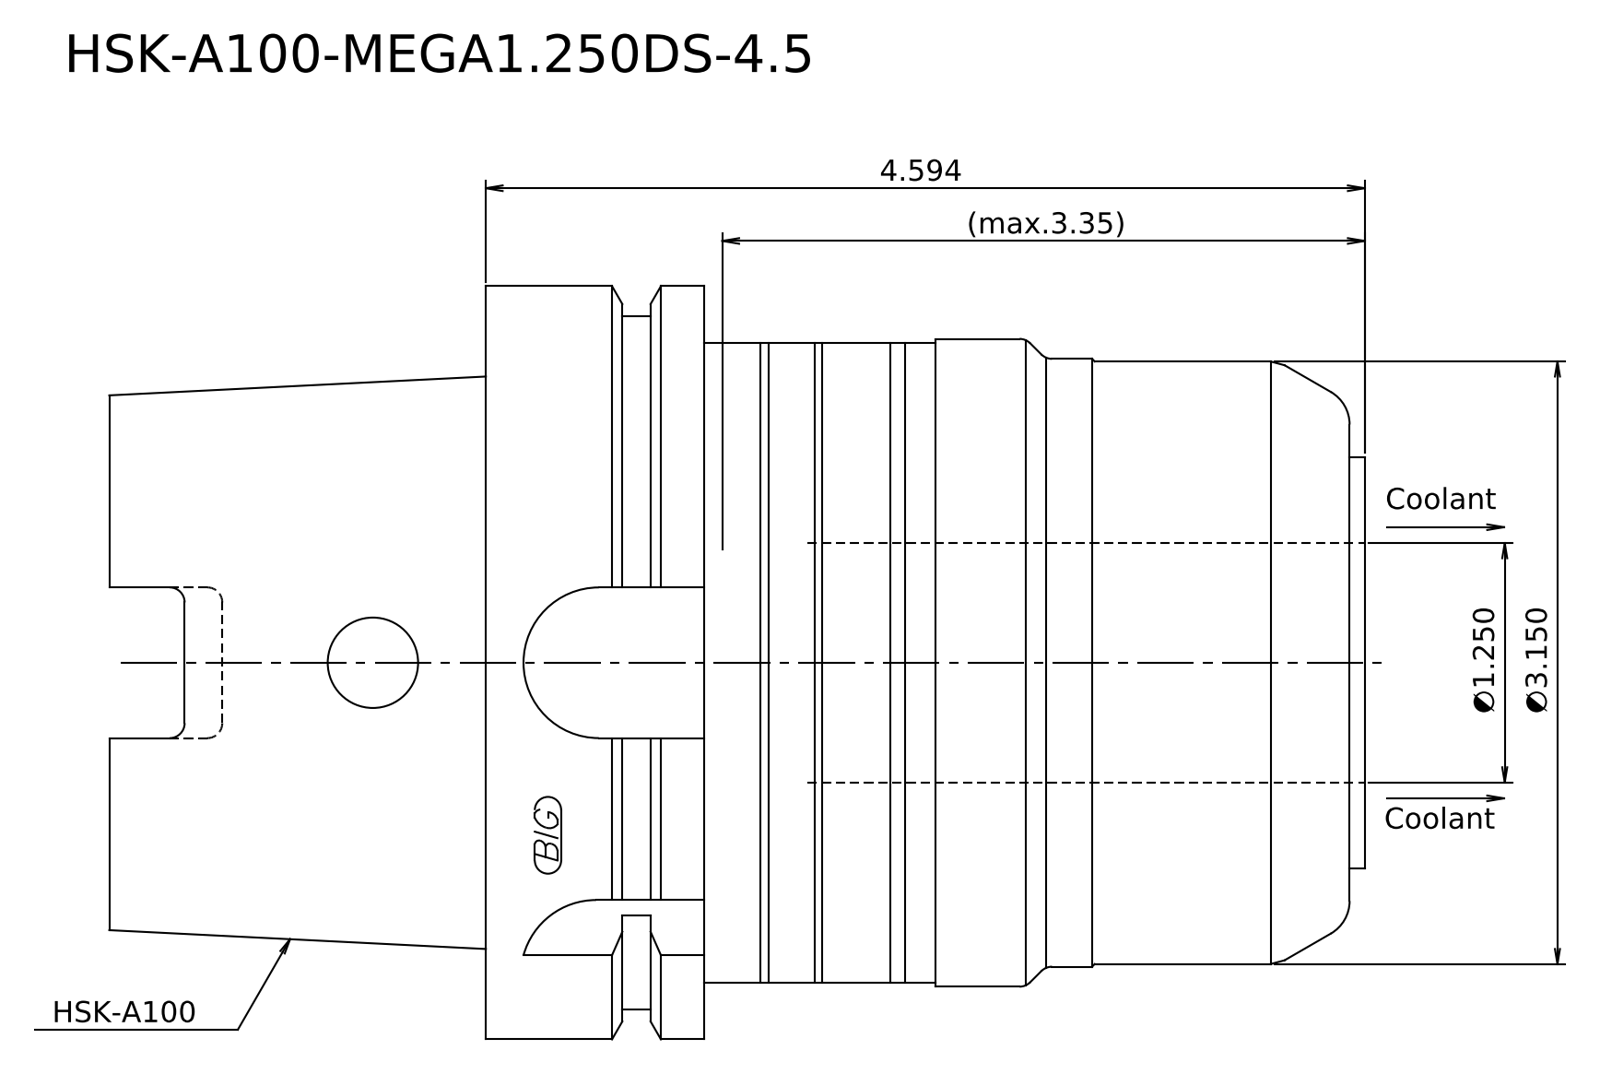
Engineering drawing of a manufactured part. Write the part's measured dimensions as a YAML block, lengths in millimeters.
step_written_by: "Kubotek KeyCreator 2011 V10.0.2 (22737) (automotive_design)"
units: millimeters
bodies: {solids: 1, faces: 23, planar: 8, cylindrical: 8, other: 7}
overall_size: [166.7, 100, 100]
volume: 894726
surface_area: 58791
round_bosses_or_shafts:
  - {diameter: 100, count: 1}
  - {diameter: 92, count: 1}
  - {diameter: 86, count: 1}
  - {diameter: 85, count: 1}
  - {diameter: 80.7, count: 1}
  - {diameter: 80, count: 1}
  - {diameter: 54.67, count: 1}
face_to_face_distances: [50, 116.7, 166.7, 87.7, 29, 79, 2, 85.7, 114.7, 164.7]
